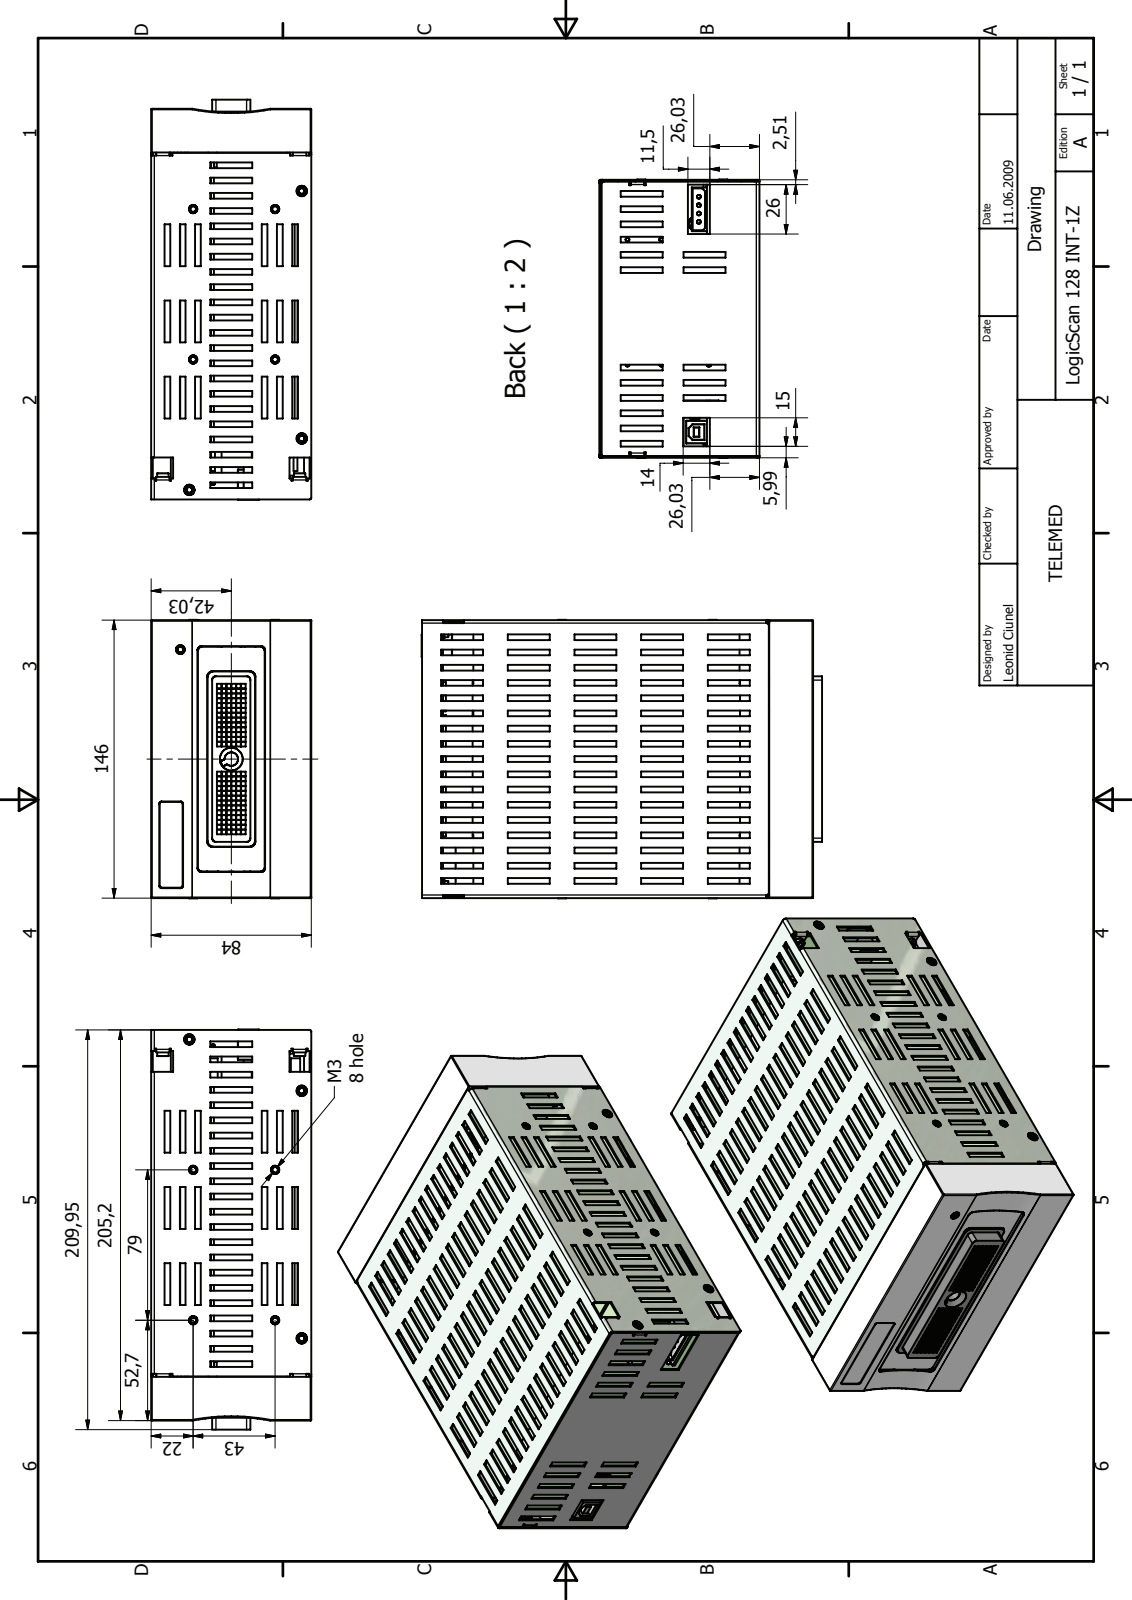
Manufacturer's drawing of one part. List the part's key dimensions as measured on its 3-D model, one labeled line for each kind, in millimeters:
Part name (STEP PRODUCT): LogicScan 128 INT-1Z; LPN-006; Sborka INT; Echo Blaster 128 FR (+8 more)
STEP written by: Autodesk Inventor 2009 (AUTOMOTIVE_DESIGN)
Units: millimetres
Bodies: 96 solids, 10440 faces (7759 planar, 429 cylindrical, 2252 other)
Overall size (bounding box): 210.17 × 146.3 × 84
Volume: 375 030 mm³ · Surface area: 588 410 mm²
Round holes (diameter × count): ⌀3.4 ×12, ⌀3 ×11, ⌀3.6 ×11, ⌀2 ×8, ⌀3.2 ×8, ⌀4.2 ×6, ⌀2.5 ×4, ⌀4 ×1
Round bosses / shafts (diameter × count): ⌀6 ×19, ⌀6.2 ×12, ⌀4.4 ×11, ⌀3 ×9, ⌀7 ×8, ⌀2 ×8, ⌀4.5 ×4
Partial cylindrical surfaces — rounded edges, fillets, slot ends (radius × count): R0.5 ×60, R1 ×26, R3 ×24, R0.3 ×18, R0.1 ×14, R0.8 ×11, R1.6 ×11, R2 ×8
Main face-to-face distances: 1.5, 0.8, 25.08, 17.7, 42.78, 18.8, 43.88, 61.58, 83.2, 13.7
Hole centre spacings: 133.99, 152, 18, 32.56, 42.98, 65.65, 68.07, 71.76
